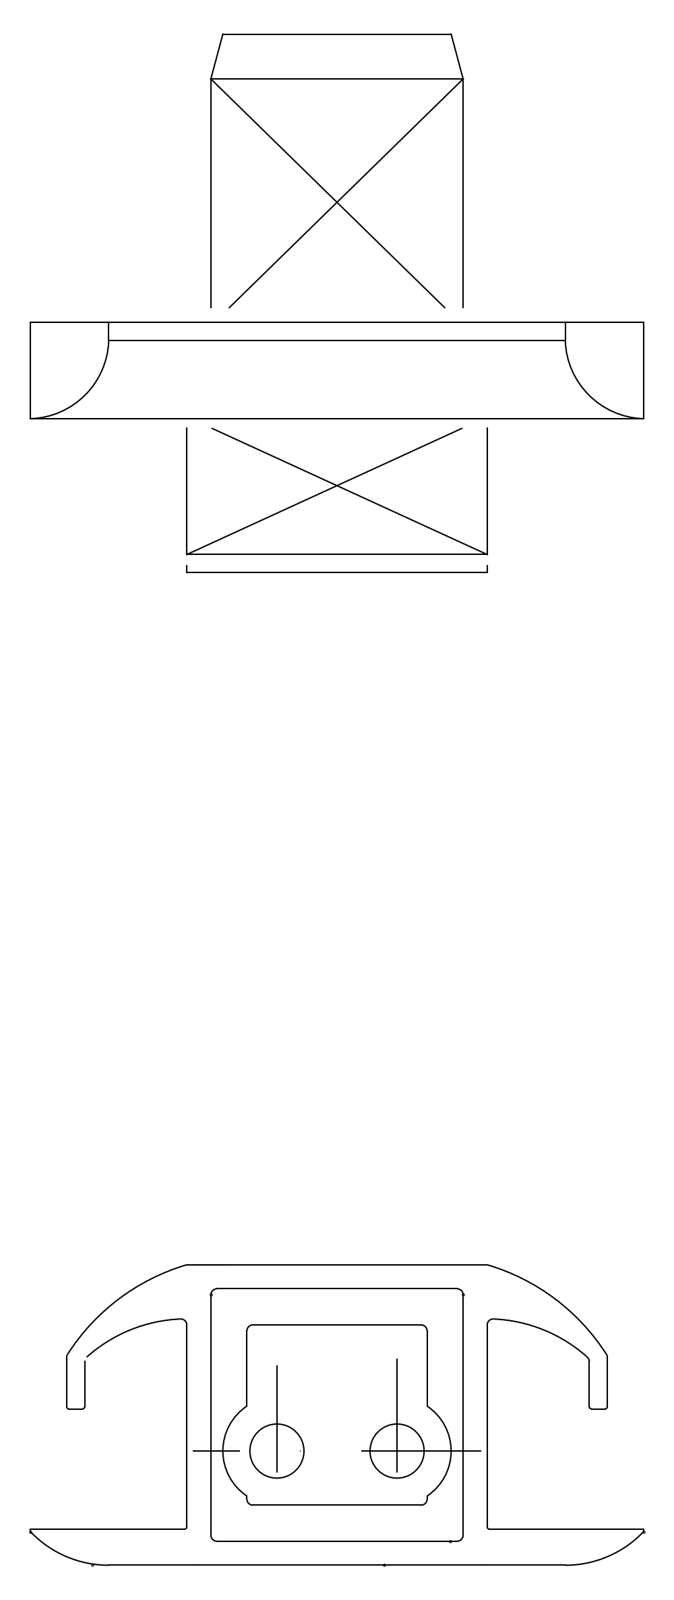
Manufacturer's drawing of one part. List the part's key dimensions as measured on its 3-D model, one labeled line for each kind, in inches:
Part name (STEP PRODUCT): XF30201G
STEP written by: Autodesk Inventor 2016 (CONFIG_CONTROL_DESIGN)
Units: inches
Bodies: 1 solid, 60 faces (42 planar, 18 cylindrical, 0 other)
Overall size (bounding box): 2.008 × 1.732 × 0.984
Volume: 0.786 in³ · Surface area: 13.71 in²
Round holes (diameter × count): ⌀0.173 ×2
Partial cylindrical surfaces — rounded edges, fillets, slot ends (radius × count): R0.118 ×4, R0.157 ×3, R0.167 ×2, R0.404 ×2, R0.475 ×2, R0.669 ×1
Main face-to-face distances: 0.079, 0.787, 0.118, 0.709, 0.197, 0.906, 0.591, 0.827, 0.394, 0.472
Hole centre spacings: 0.394
